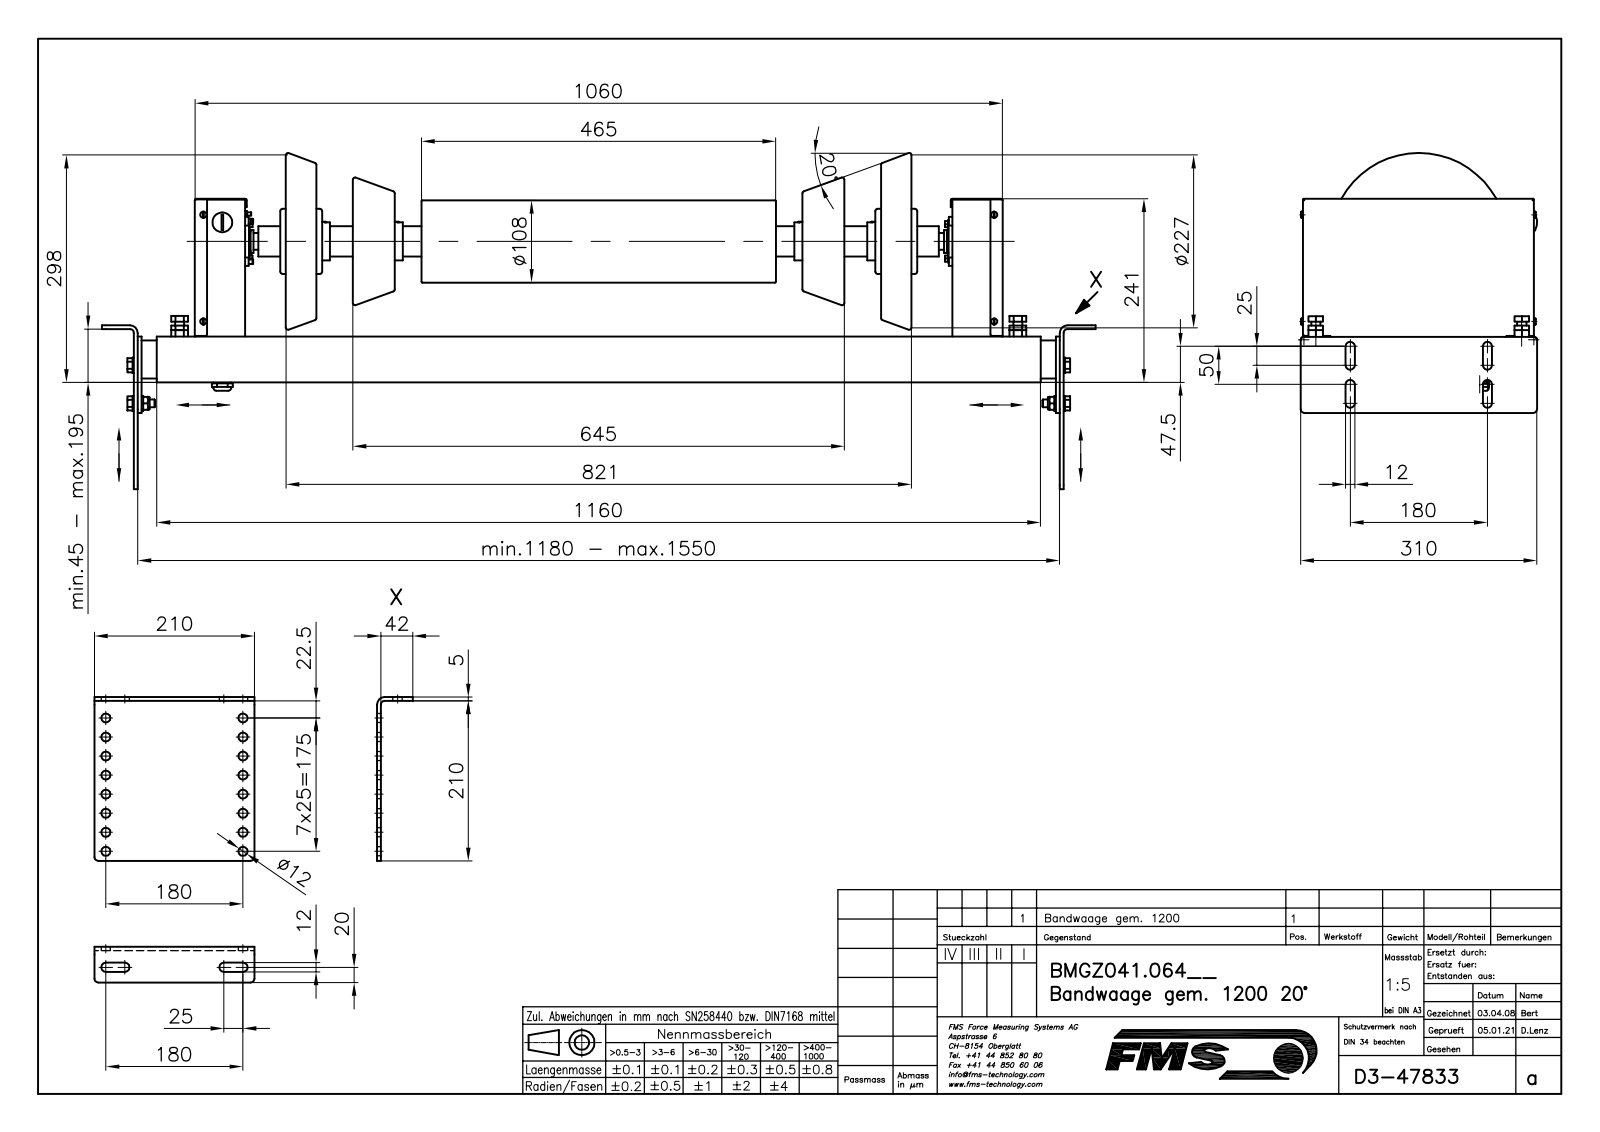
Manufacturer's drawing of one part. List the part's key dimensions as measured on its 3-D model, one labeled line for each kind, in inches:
Part name (STEP PRODUCT): B47833_STP; B50109; 6KT-SCHRAUBE_M12X30; ZYL_SCHR__M4X8 (+8 more)
STEP written by: Mechanical Desktop 2009 (CONFIG_CONTROL_DESIGN)
Units: inches
Bodies: 179 solids, 2924 faces (1427 planar, 1058 cylindrical, 439 other)
Overall size (bounding box): 51.339 × 17.362 × 12.213
Volume: 536.2 in³ · Surface area: 5 853 in²
Round holes (diameter × count): ⌀0.472 ×17, ⌀0.197 ×6, ⌀0.138 ×4, ⌀0.193 ×4, ⌀0.252 ×4, ⌀0.272 ×4, ⌀0.342 ×4, ⌀0.344 ×4, ⌀0.394 ×4, ⌀0.413 ×4, ⌀0.42 ×4, ⌀0.583 ×4
Round bosses / shafts (diameter × count): ⌀0.472 ×11, ⌀0.323 ×8, ⌀0.165 ×8, ⌀0.787 ×6, ⌀0.394 ×6, ⌀0.315 ×6, ⌀0.197 ×5, ⌀0.63 ×4
Partial cylindrical surfaces — rounded edges, fillets, slot ends (radius × count): R0.079 ×34, R0.039 ×24, R0.157 ×16, R0.197 ×16, R0.236 ×12, R0.138 ×8, R0.089 ×6, R0.02 ×4
Main face-to-face distances: 0.157, 0.197, 0.039, 10.63, 1.417, 0.118, 2.559, 10.472, 1.26, 2.598
Hole centre spacings: 0.984, 7.155, 1.969, 7.355, 2.953, 7.677, 3.937, 7.087
